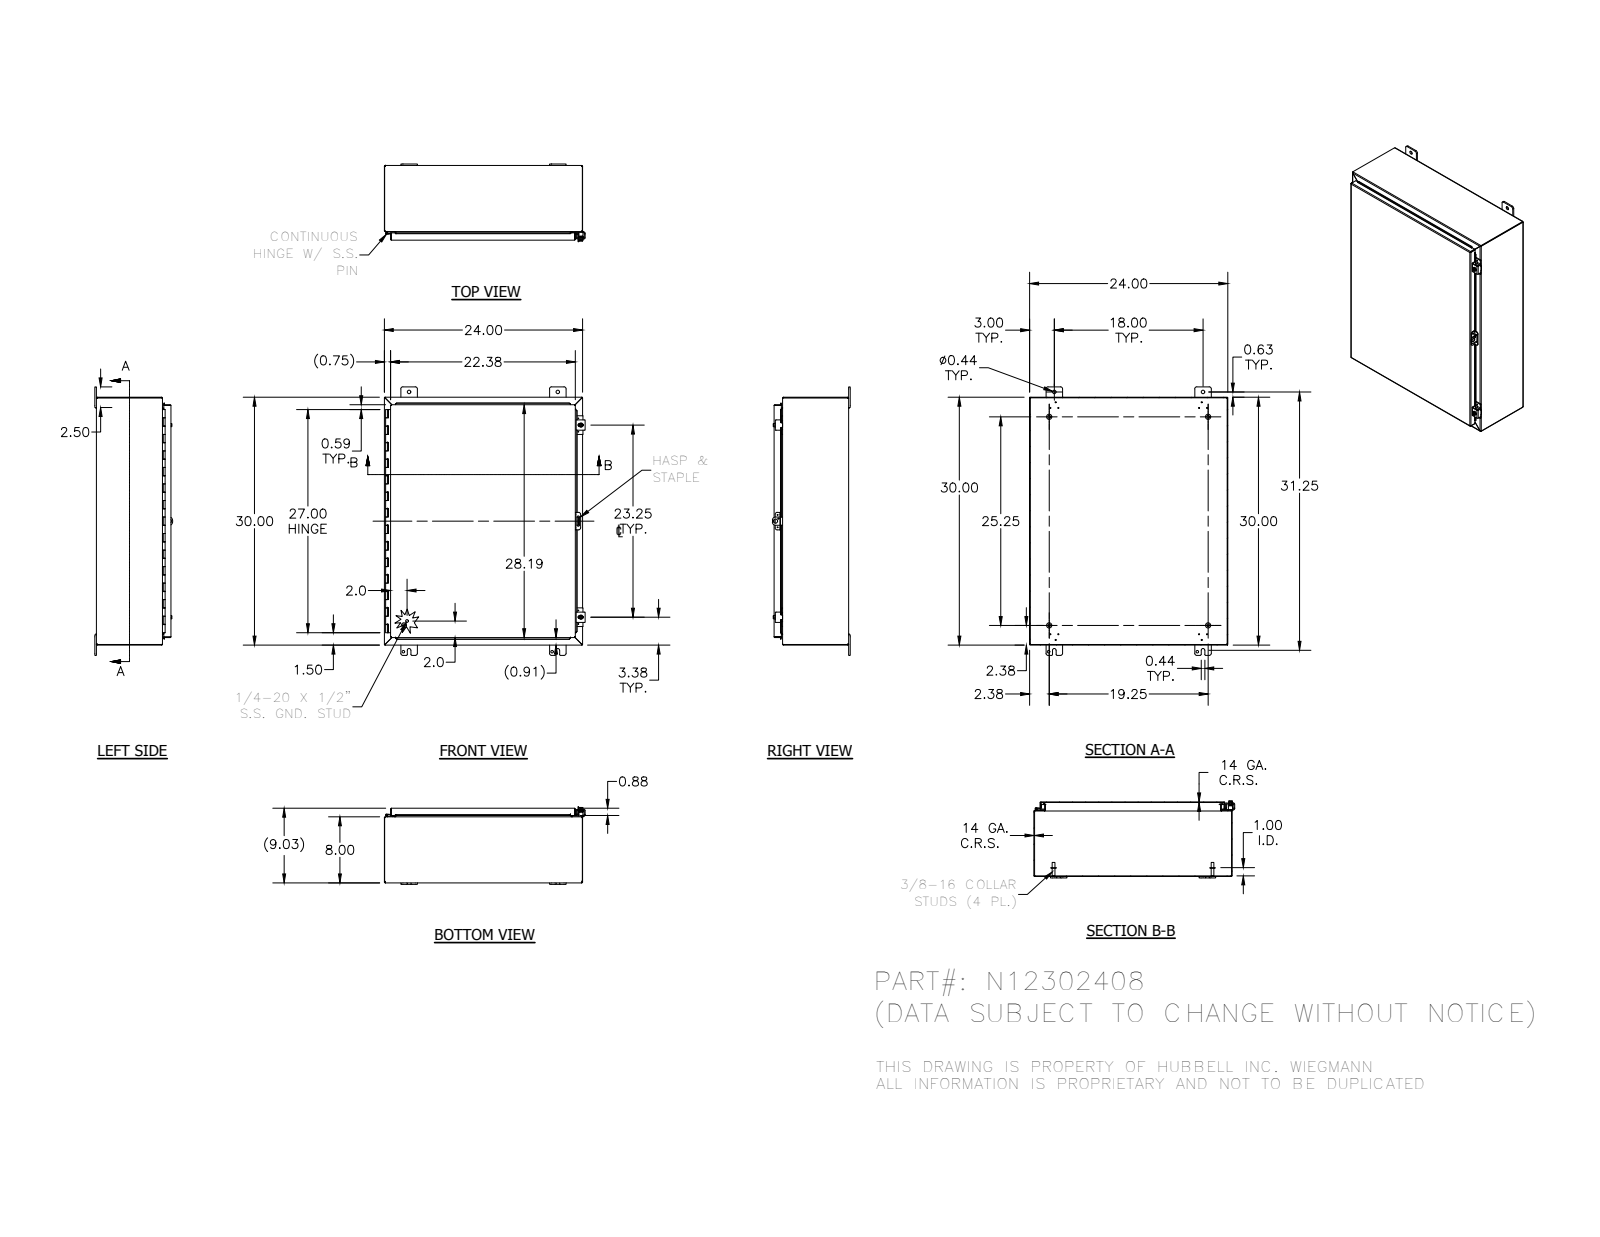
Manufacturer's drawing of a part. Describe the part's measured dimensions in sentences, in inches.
The part is named "N12302408; 34840; 38420; N12302408BKP (+8 more)". Its 3-D file was written by "Autodesk Inventor 2012 (AUTOMOTIVE_DESIGN)". It is 27 solids with 1033 faces: 566 planar, 350 cylindrical and 117 other. Overall it measures 32.5 by 24.311 by 9.41 inches. Its volume is 206 cubic inches and its surface area 5 400 square inches. Round holes: 12 of diameter 0.12, 7 of diameter 0.11, 4 of diameter 0.313, 4 of diameter 0.438, 2 of diameter 0.211, 2 of diameter 0.281, 2 of diameter 0.3, 1 of diameter 0.125, 1 of diameter 0.156, 1 of diameter 0.5. Round bosses or shafts: 4 of diameter 0.625, 4 of diameter 0.33, 4 of diameter 0.25, 2 of diameter 0.52, 2 of diameter 0.5, 2 of diameter 0.35, 2 of diameter 0.115, 1 of diameter 0.337. Partial cylindrical surfaces (rounded edges, fillets, slot ends): 27 of radius 0.03, 25 of radius 0.063, 25 of radius 0.125, 25 of radius 0.25, 23 of radius 0.031, 23 of radius 0.105, 8 of radius 0.07, 4 of radius 0.1. The main face-to-face distances are 0.074, 8.959, 8.885, 9.033, 23.926, 29.926, 7.926, 1.033, 23.852, 24. The hole center spacings are 18, 0.759, 0.94, 0.969, 1.995, 17.37, 18.339, 27.38.
